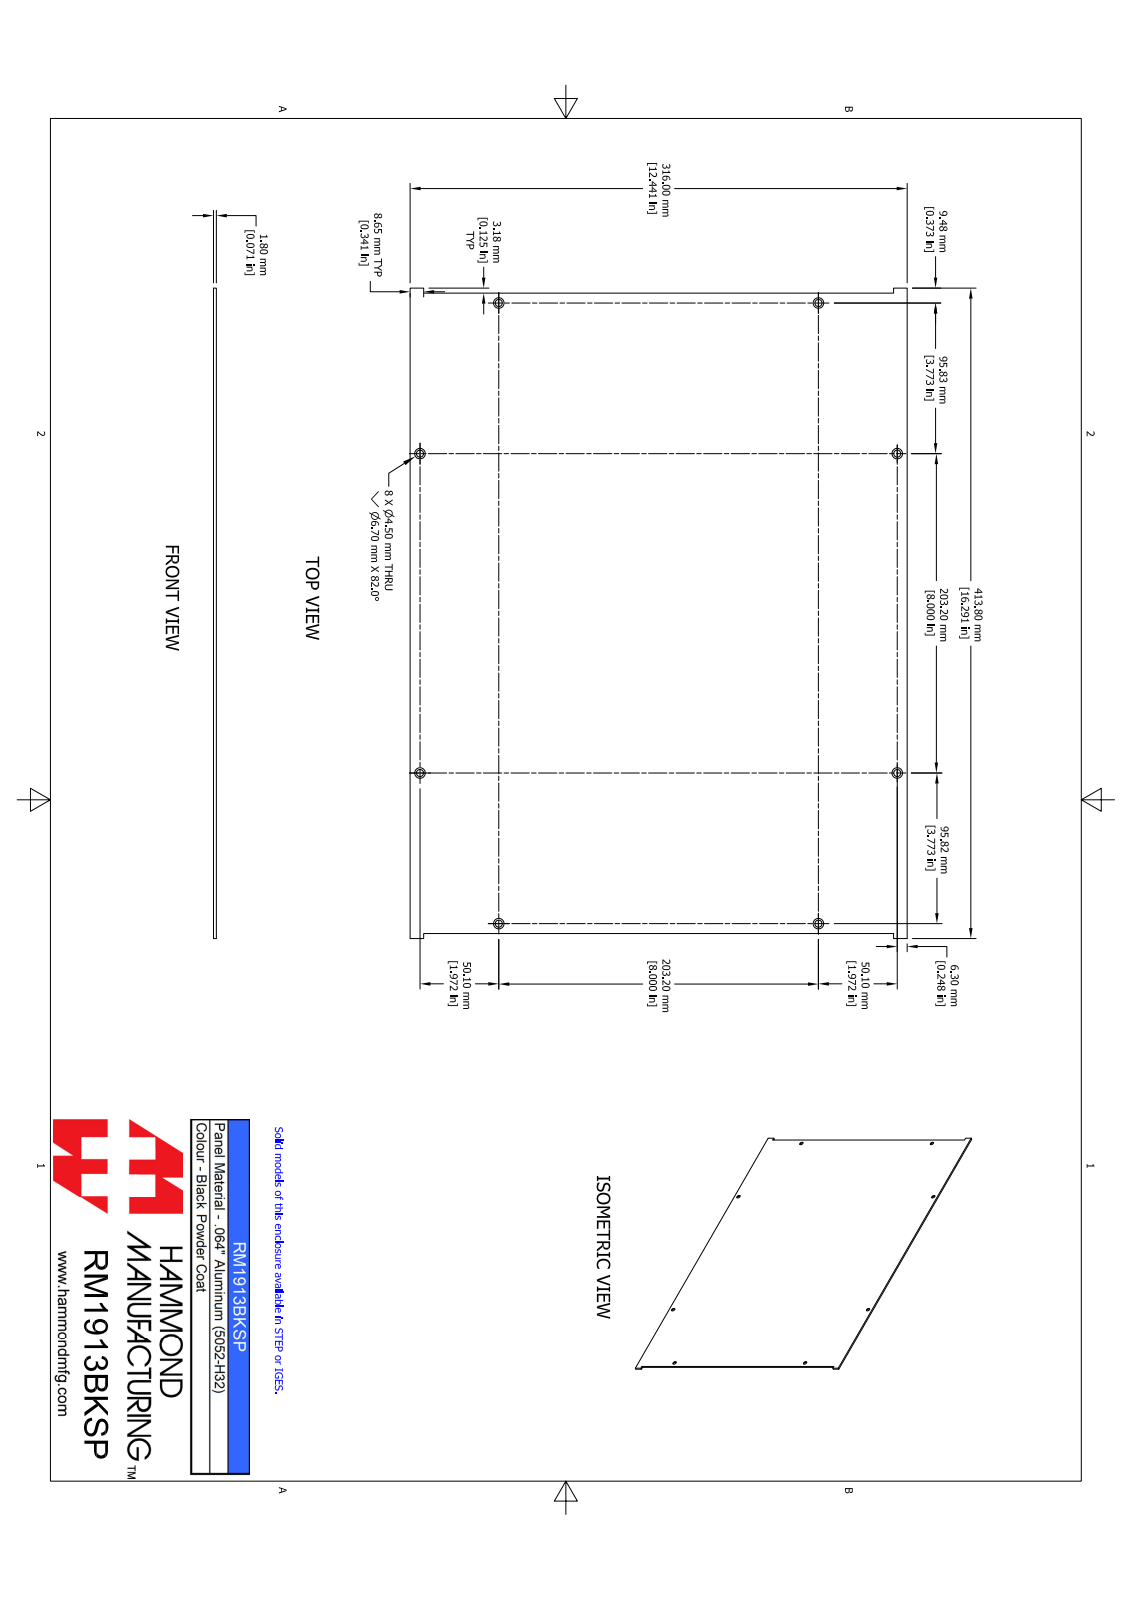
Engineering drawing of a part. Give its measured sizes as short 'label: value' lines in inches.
name: RM1913BKSP
written by: SolidWorks 2021 (AUTOMOTIVE_DESIGN)
unit: in
bodies: 1 solid, 30 faces (14 planar, 8 cylindrical, 8 other)
size: 16.291 × 12.441 × 0.071
volume: 14.14 in³; area: 403.4 in²
holes: 8× ⌀0.177
face distances: 0.071, 12.441, 16.041, 16.166, 0.125, 0.125, 16.167, 16.291, 0.341, 12.1
hole spacings: 4.257, 8, 10.662, 11.937, 15.428, 11.945, 14.376, 15.545
